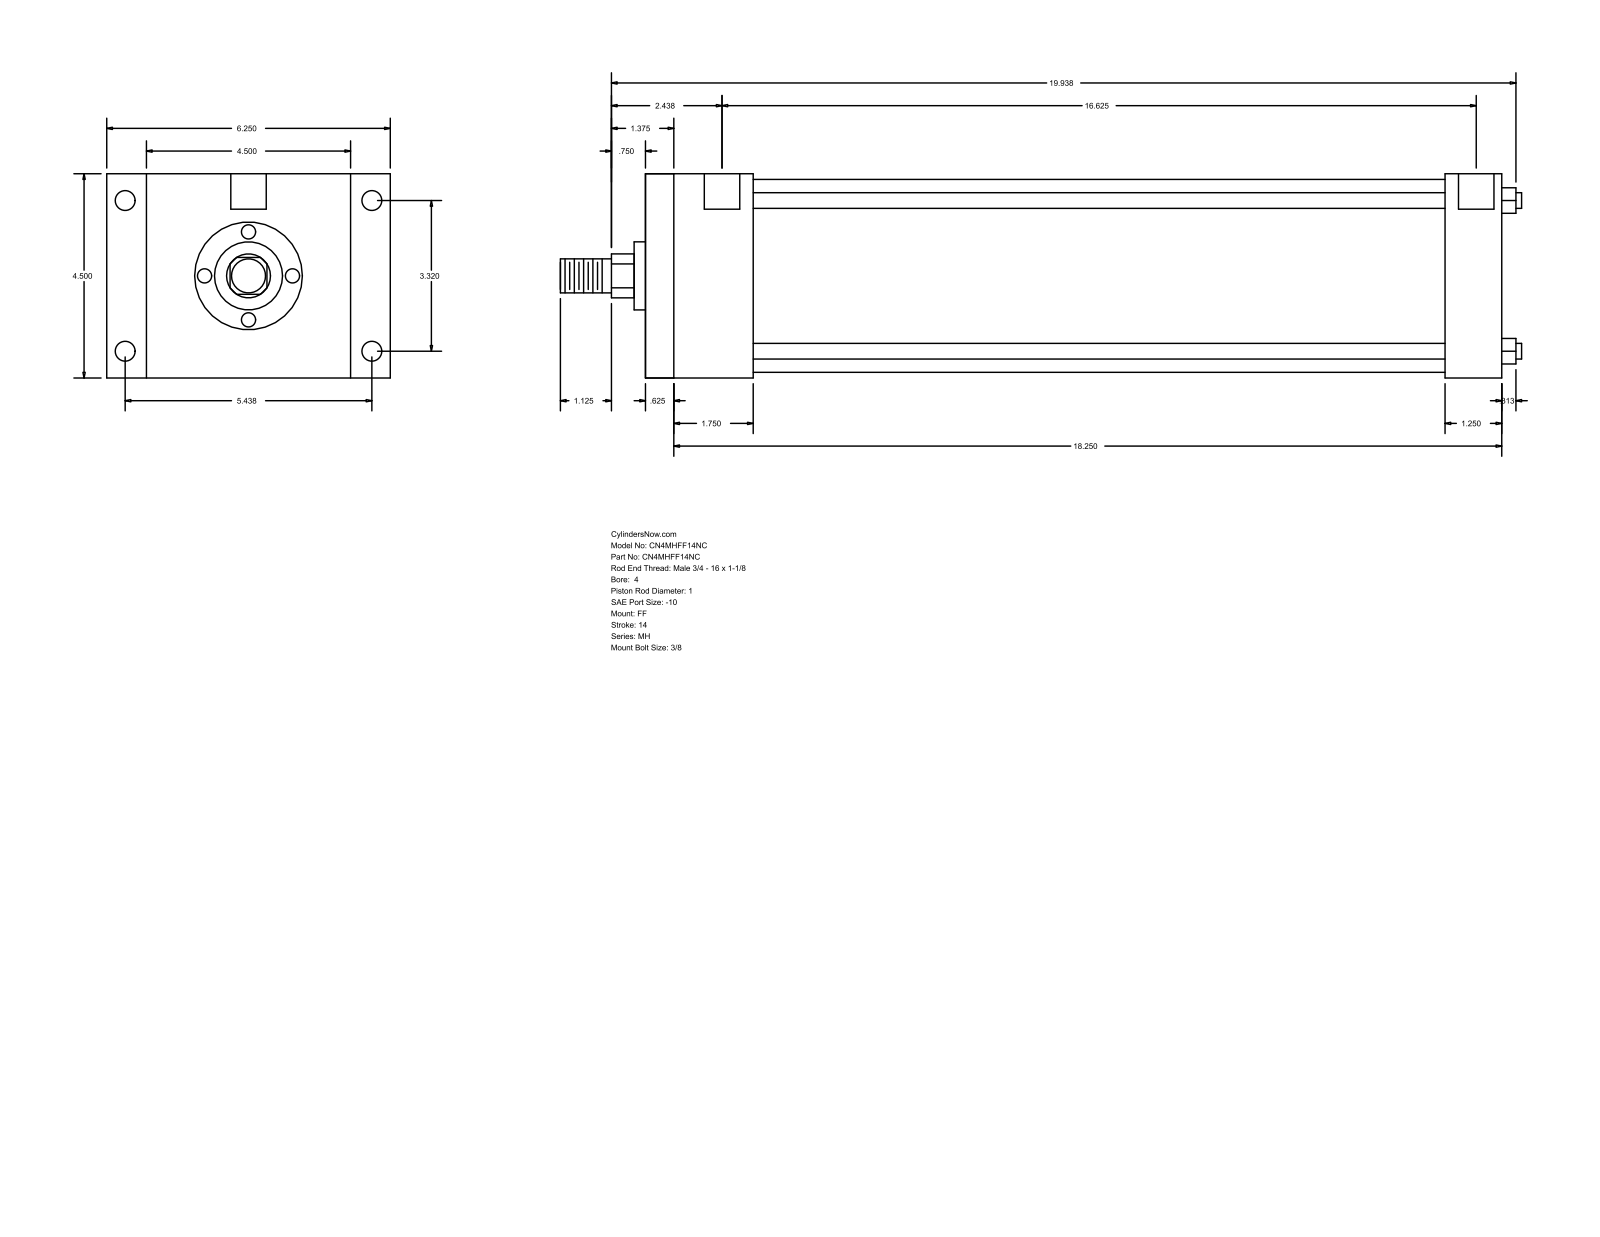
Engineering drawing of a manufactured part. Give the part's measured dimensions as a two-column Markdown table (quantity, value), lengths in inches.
| quantity | value |
| --- | --- |
| part name | MH_FF__0400_1 |
| STEP written by | GSSL Pune (CONFIG_CONTROL_DESIGN) |
| units | inches |
| bodies | 0 solids, 92 faces (64 planar, 28 cylindrical, 0 other) |
| overall size | 21.187 × 6.25 × 4.5 |
| round holes (diameter × count) | 0.344 × 4, 0.438 × 4, 0.781 × 2 |
| round bosses / shafts (diameter × count) | 0.345 × 4, 4.25 × 1, 1.5 × 1, 1 × 1, 0.75 × 1 |
| partial cylindrical surfaces (radius × count) | 0.484 × 1 |
| main face-to-face distances | 4.5, 18.875, 0.625, 18.25, 2.375, 1.75, 16.5, 17.625, 17, 15.25 |
| hole center spacings | 0.062, 3.32, 5.438, 6.371, 16.687, 16.75, 16.625 |
